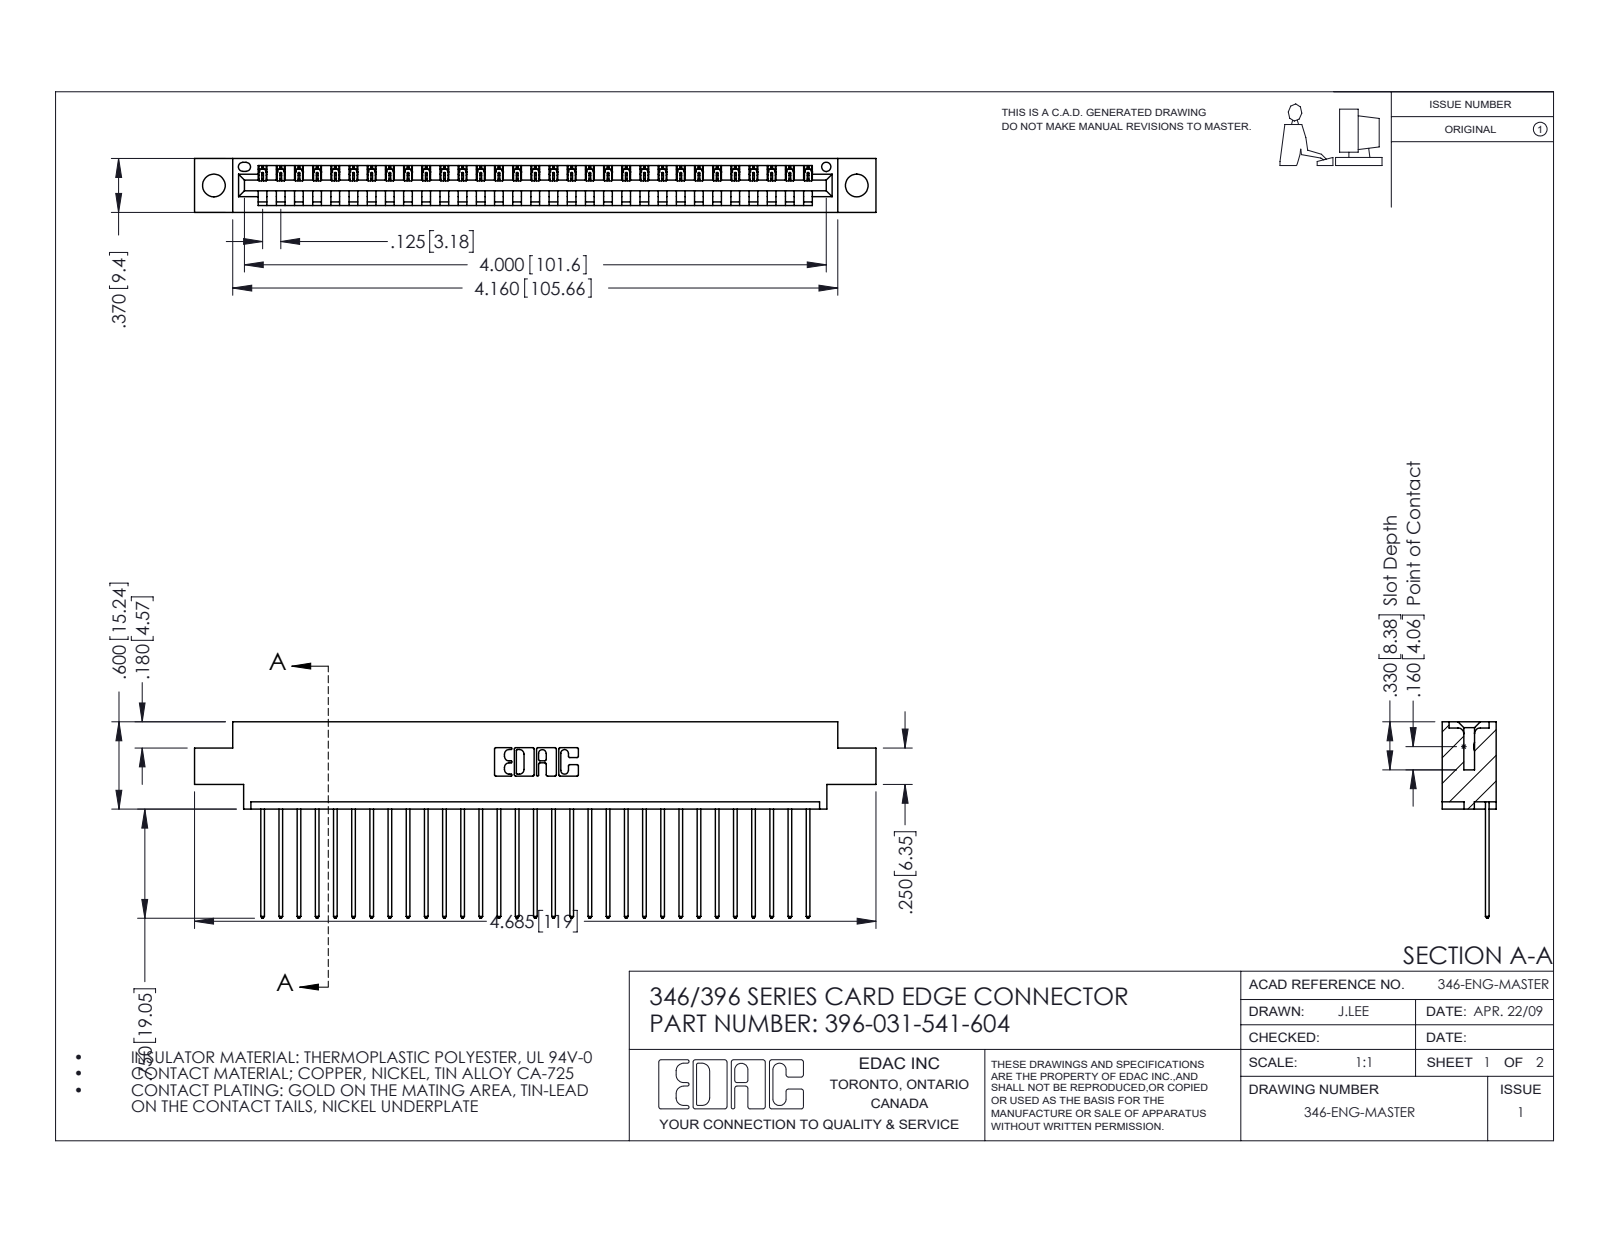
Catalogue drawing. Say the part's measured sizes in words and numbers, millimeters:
The part is named "345-292-001_345-293-141; 346 Part_0.170 Offset - 0.156 Dia-TH; 396-031-541-604". Its 3-D file was written by "SolidWorks 2016 (CONFIG_CONTROL_DESIGN)". It is 32 solids with 1924 faces: 1320 planar, 604 cylindrical and 0 other. Overall it measures 119 by 34.3 by 9.4 millimeters. Its volume is 11 200 cubic millimeters and its surface area 14 430 square millimeters. Round holes: 2 of diameter 4, 1 of diameter 1.6. Partial cylindrical surfaces (rounded edges, fillets, slot ends): 62 of radius 0.2, 62 of radius 0.3, 22 of radius 0.3, 6 of radius 0.2, 6 of radius 0.8, 3 of radius 0.7, 2 of radius 0.8, 2 of radius 1. The main face-to-face distances are 1.2, 8.2, 9.4, 6.4, 1.8, 7.6, 0.6, 3.8, 5.6, 2.5. The hole center spacings are 6.2, 107, 112.3.
